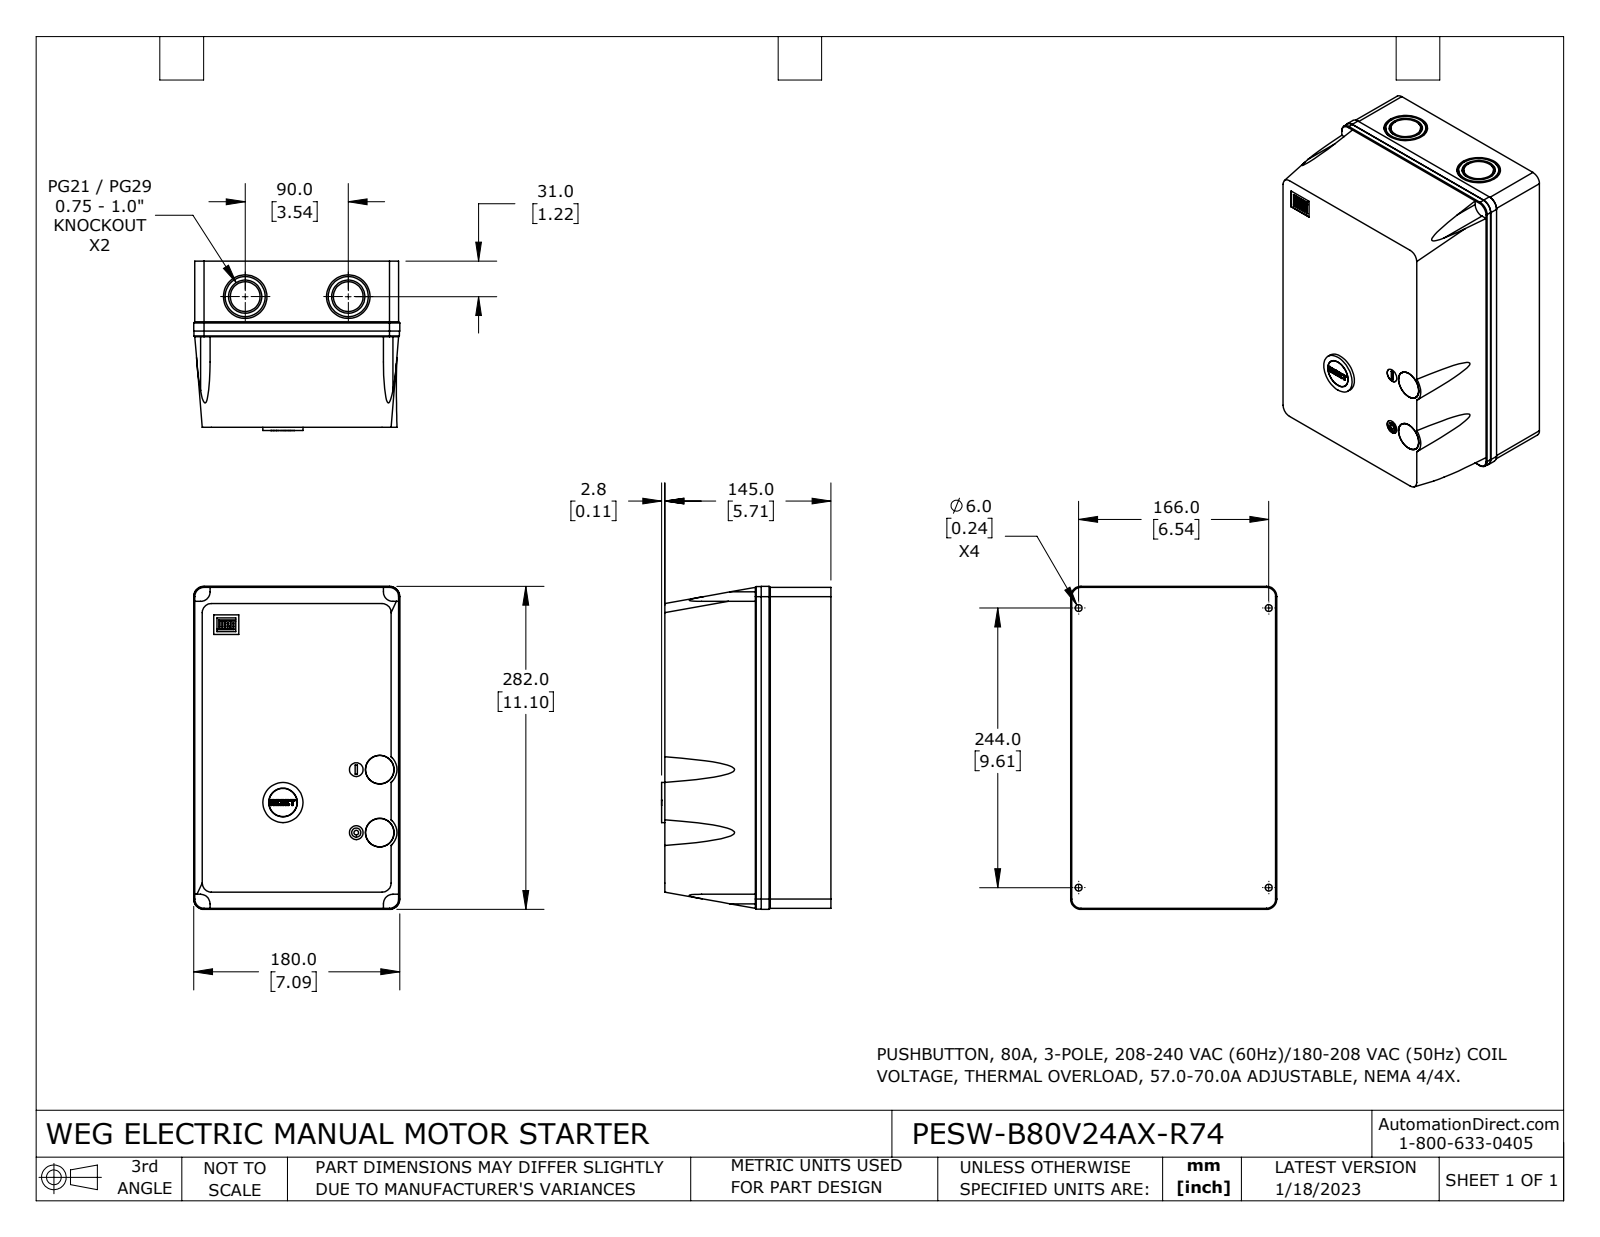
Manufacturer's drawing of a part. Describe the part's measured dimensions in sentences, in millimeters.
The part is named "PESW-B80V24AX-R74". Its 3-D file was written by "SolidWorks 2021 (CONFIG_CONTROL_DESIGN)". It is 3 solids with 286 faces: 130 planar, 144 cylindrical and 12 other. Overall it measures 282 by 180 by 147.9 millimeters. Its volume is 7 014 000 cubic millimeters and its surface area 232 257 square millimeters. Round holes: 4 of diameter 6, 3 of diameter 25, 2 of diameter 12, 2 of diameter 29, 2 of diameter 38, 1 of diameter 4, 1 of diameter 30.5. Round bosses or shafts: 3 of diameter 35, 2 of diameter 26, 2 of diameter 24.8, 1 of diameter 30.3, 1 of diameter 24.6, 1 of diameter 14, 1 of diameter 8. Partial cylindrical surfaces (rounded edges, fillets, slot ends): 34 of radius 0.1, 4 of radius 8, 4 of radius 8.3, 4 of radius 8.7, 4 of radius 9, 1 of radius 1.6. The main face-to-face distances are 145, 178, 280, 1, 0.7, 179, 179.7, 178.7, 281, 180. The hole center spacings are 20.5, 55, 58.7, 166, 244, 295.11, 49.14, 57.14.
